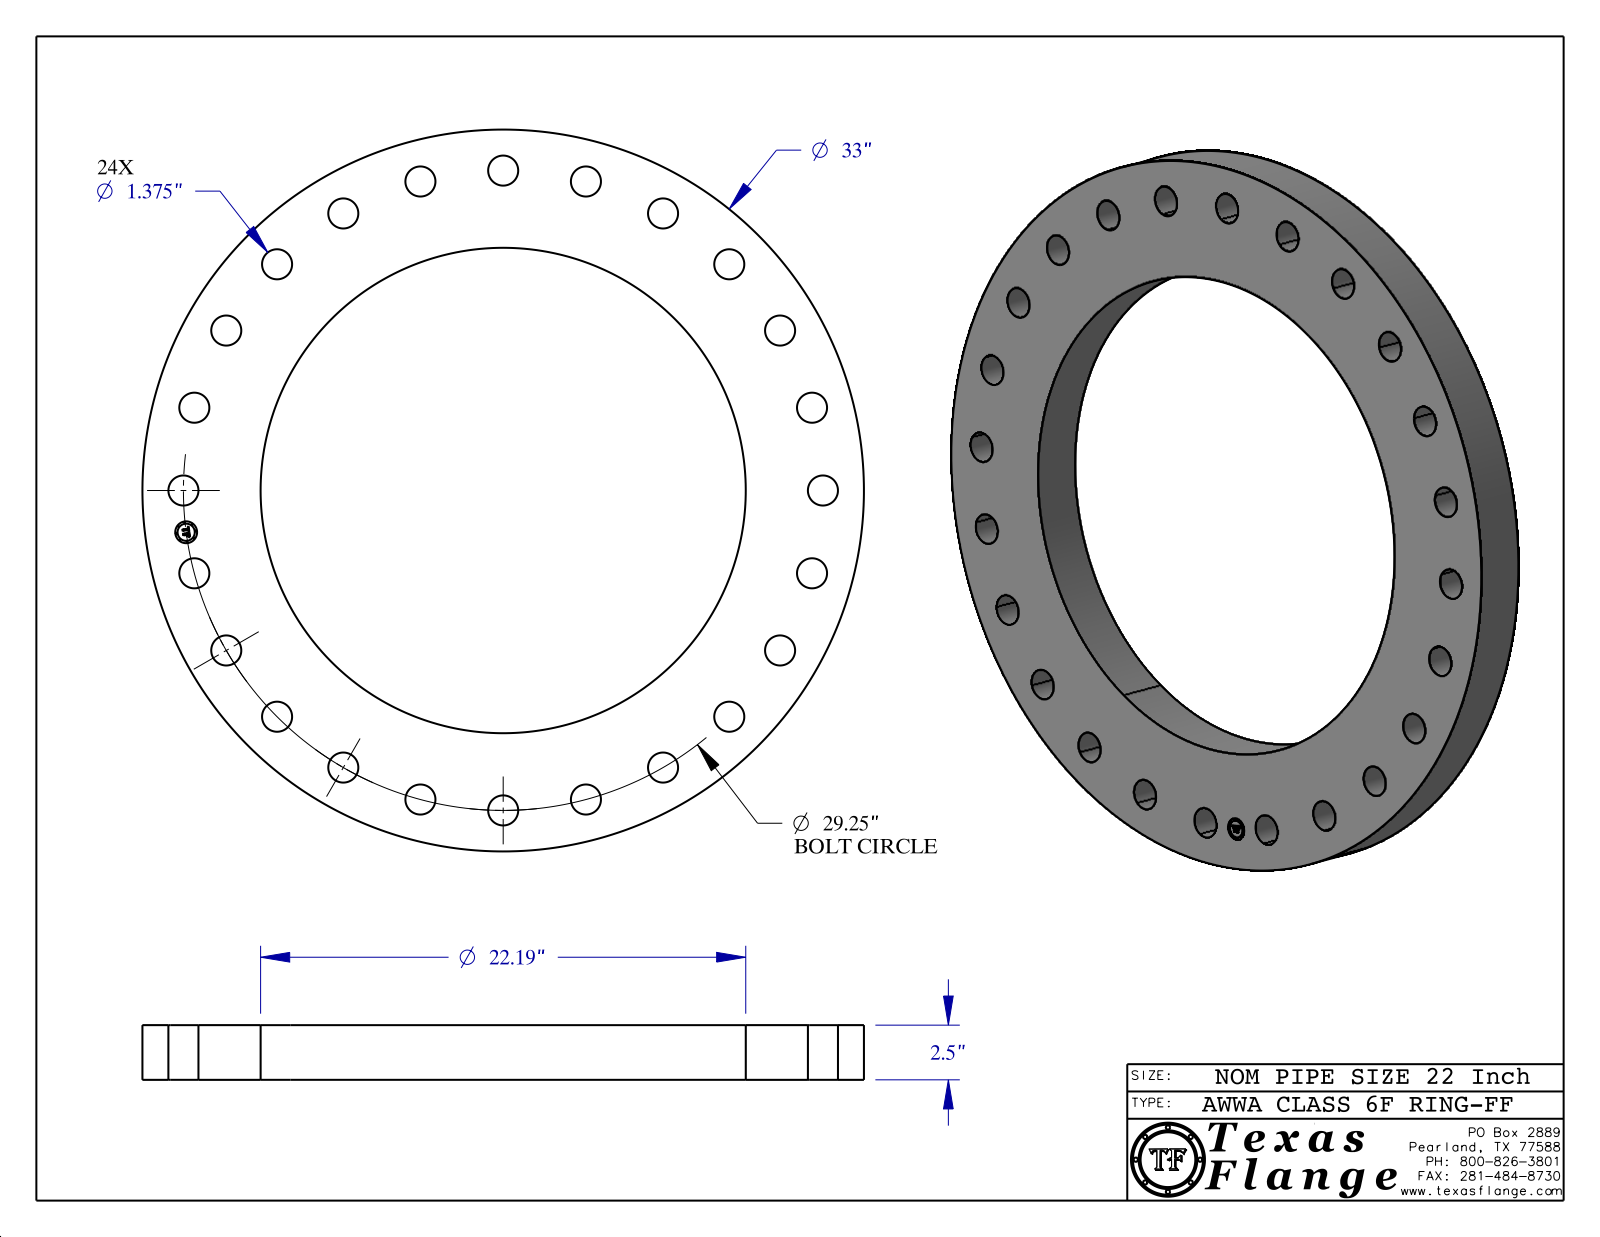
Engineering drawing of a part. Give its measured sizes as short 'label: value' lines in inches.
name: AWWA Class 6F-RING-FF
written by: CATIA V5 STEP AP214 (AUTOMOTIVE_DESIGN)
unit: in
bodies: 1 solid, 439 faces (367 planar, 72 cylindrical, 0 other)
size: 33 × 33 × 2.5
volume: 1 082 in³; area: 1 559 in²
holes: 24× ⌀1.375, 1× ⌀1, 1× ⌀22.19
bosses: 8× ⌀0.061, 1× ⌀33, 1× ⌀0.788
face distances: 2.5, 0.015, 2.485, 0.298, 0.292, 0.055, 0.193, 0.248, 0.044, 0.15
hole spacings: 14.625, 27.024, 7.57, 20.683, 3.818, 11.194, 17.806, 23.206
